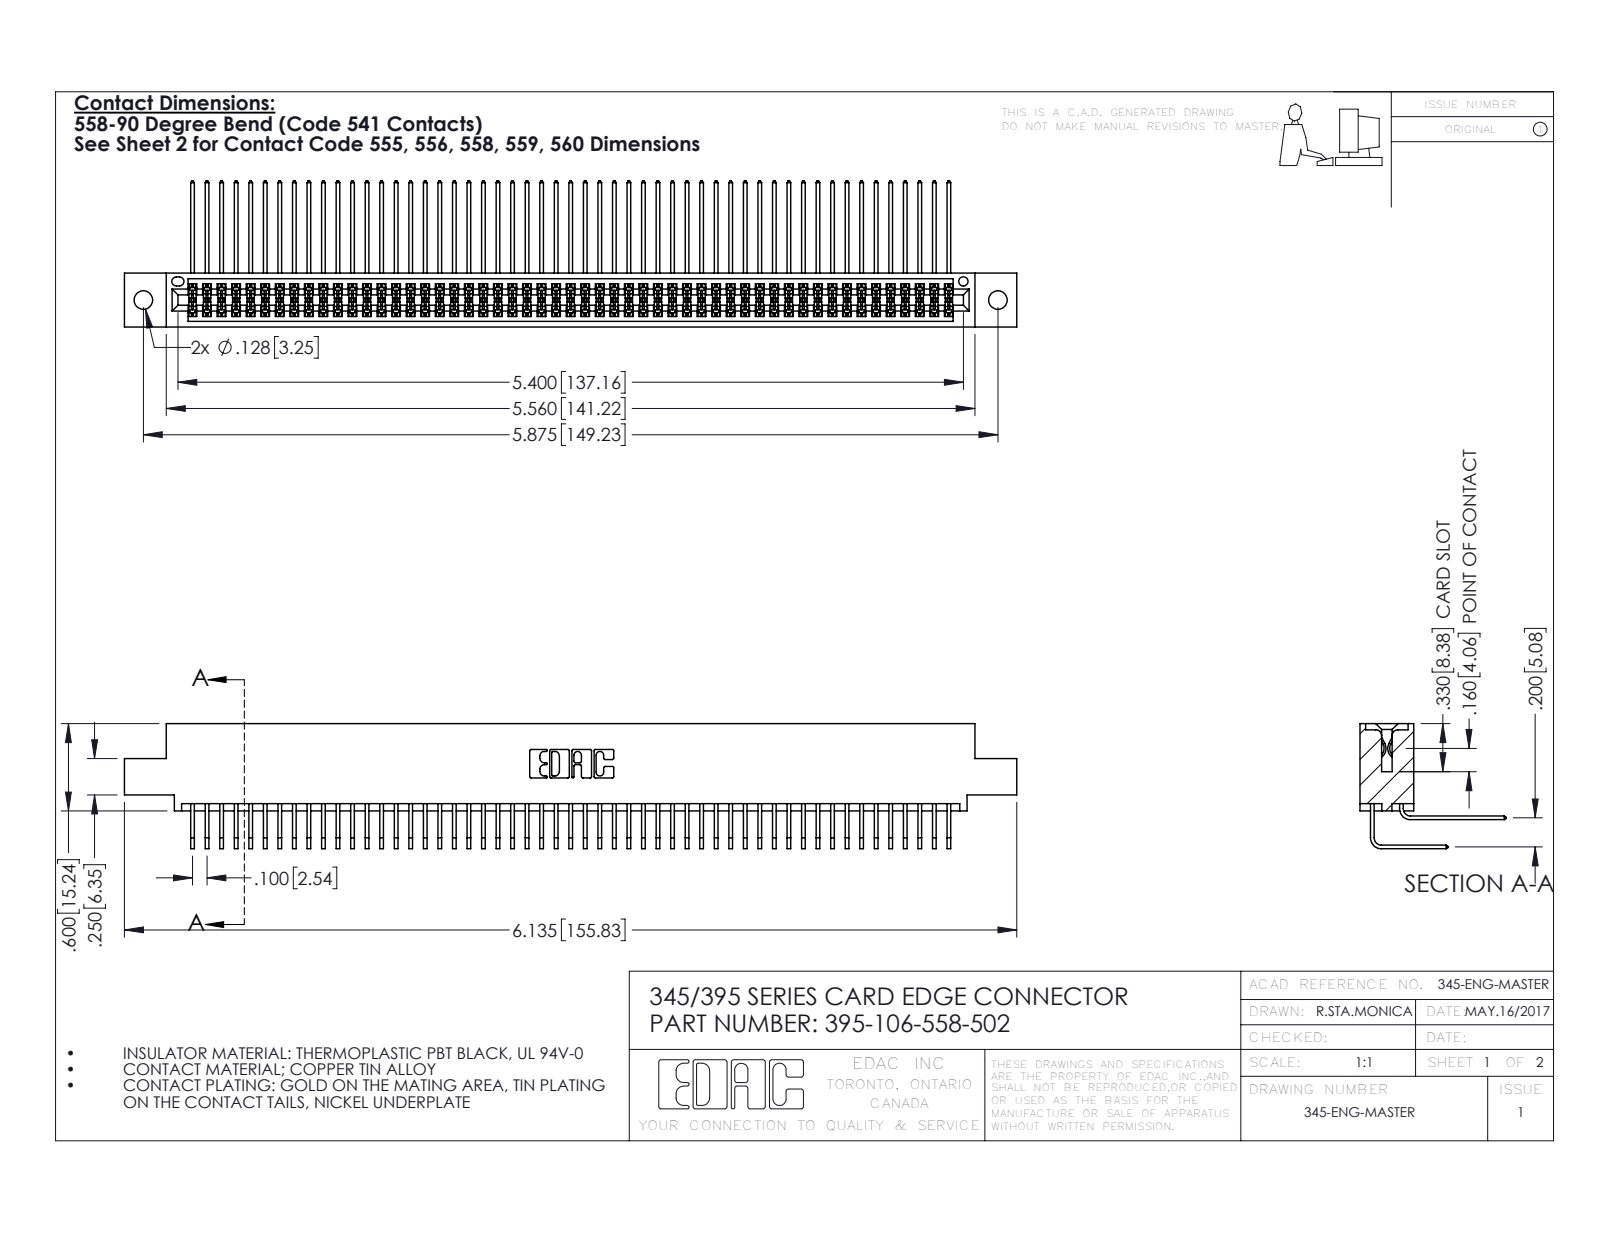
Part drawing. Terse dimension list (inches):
name: 345-292-001_558 Tail - 2; 395-106-558-502; 345 Part_0.110 Offset - 0.128 Dia; 345-292-001_558 559 Tail - 1
written by: SolidWorks 2016 (CONFIG_CONTROL_DESIGN)
unit: in
bodies: 107 solids, 5642 faces (3794 planar, 1848 cylindrical, 0 other)
size: 6.135 × 1.005 × 0.859
volume: 0.961 in³; area: 40.57 in²
holes: 2× ⌀0.128, 1× ⌀0.064
rounds: 160× R0.006, 22× R0.01, 6× R0.007, 6× R0.031, 3× R0.026, 2× R0.014, 2× R0.019, 2× R0.022
face distances: 0.072, 0.298, 0.2, 0.37, 0.098, 0.272, 0.025, 0.225, 0.025, 0.175
hole spacings: 0.27, 5.639, 5.875
